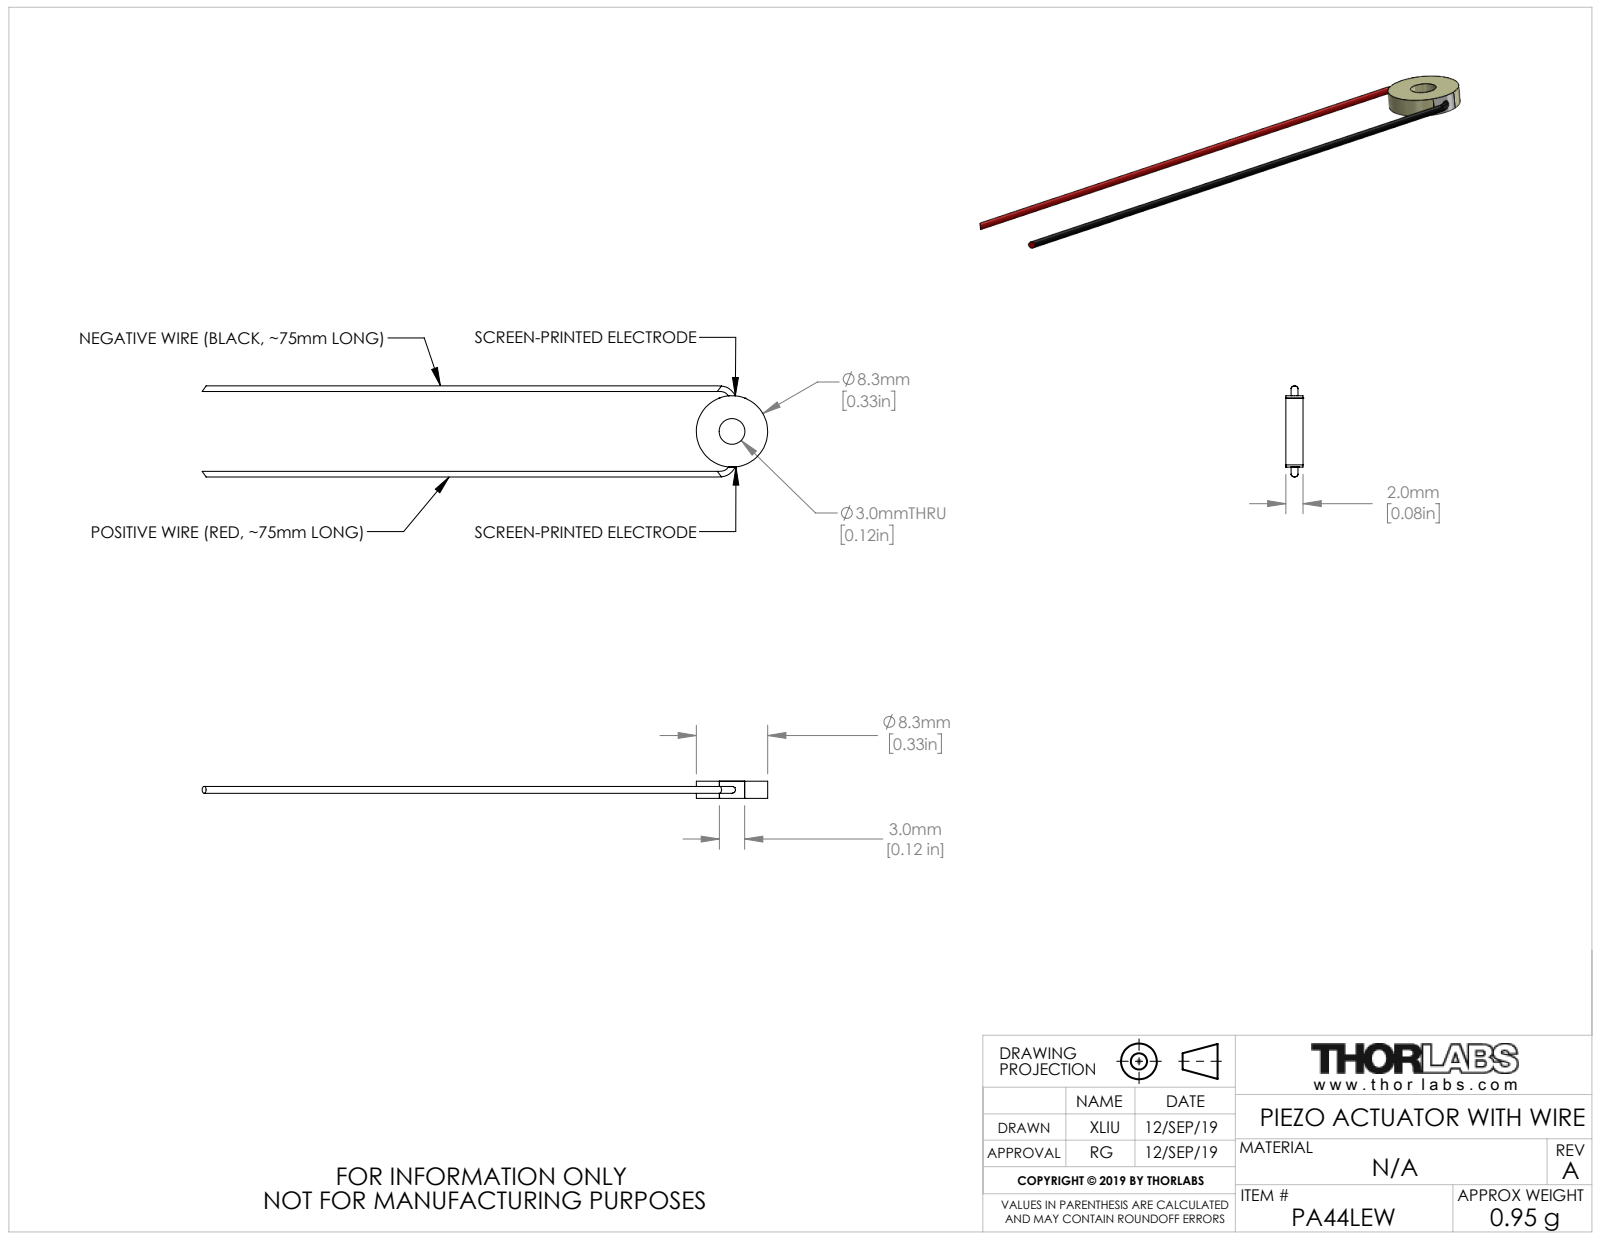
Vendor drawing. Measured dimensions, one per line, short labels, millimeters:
name: CTN009775
written by: SolidWorks 2016 (AUTOMOTIVE_DESIGN)
unit: mm
bodies: 1 solid, 38 faces (13 planar, 9 cylindrical, 16 other)
size: 65.83 × 10.61 × 2
volume: 145 mm³; area: 449 mm²
holes: 1× ⌀3
bosses: 1× ⌀8.3
rounds: 1× R4.14, 1× R4.16
face distances: 2, 8.3, 1.99
